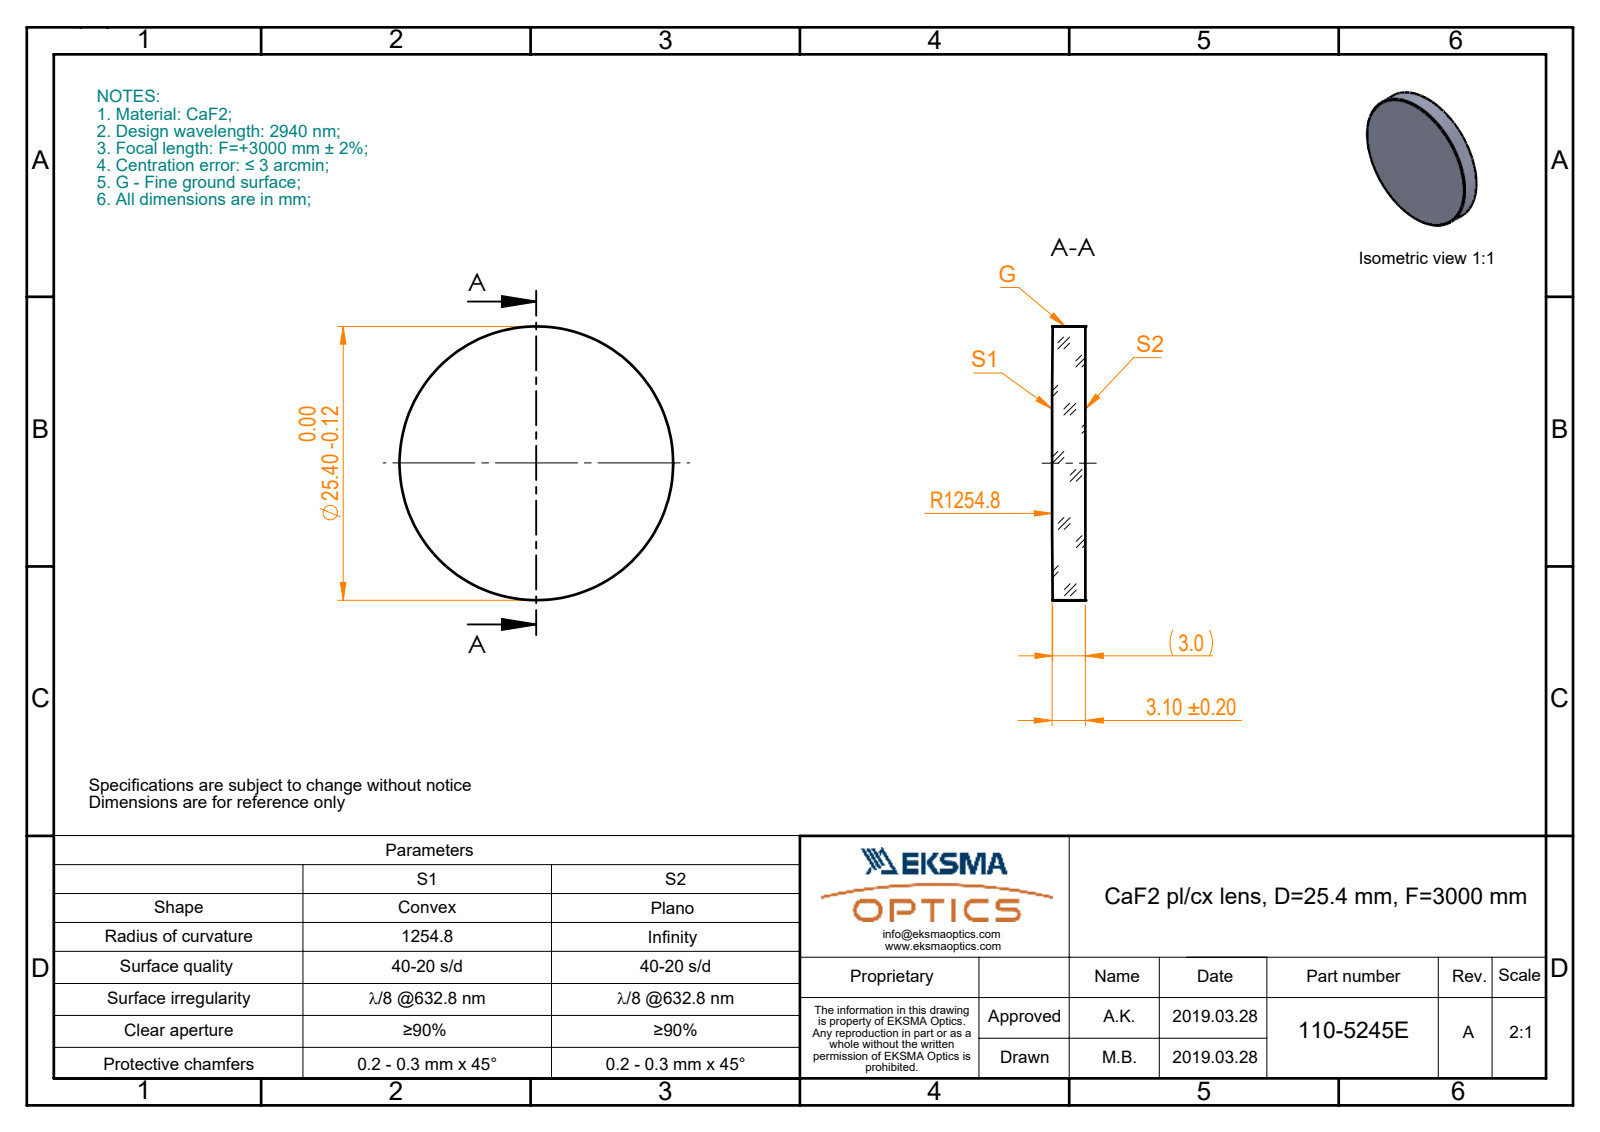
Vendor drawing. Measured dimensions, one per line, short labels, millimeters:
name: 110-5245E CaF2 pl-cx 25.4 F3000
written by: SolidWorks 2017 (CONFIG_CONTROL_DESIGN)
unit: mm
bodies: 1 solid, 5 faces (1 planar, 2 cylindrical, 2 other)
size: 25.4 × 25.4 × 3.1
volume: 1 555 mm³; area: 1 256 mm²
bosses: 1× ⌀25.4
